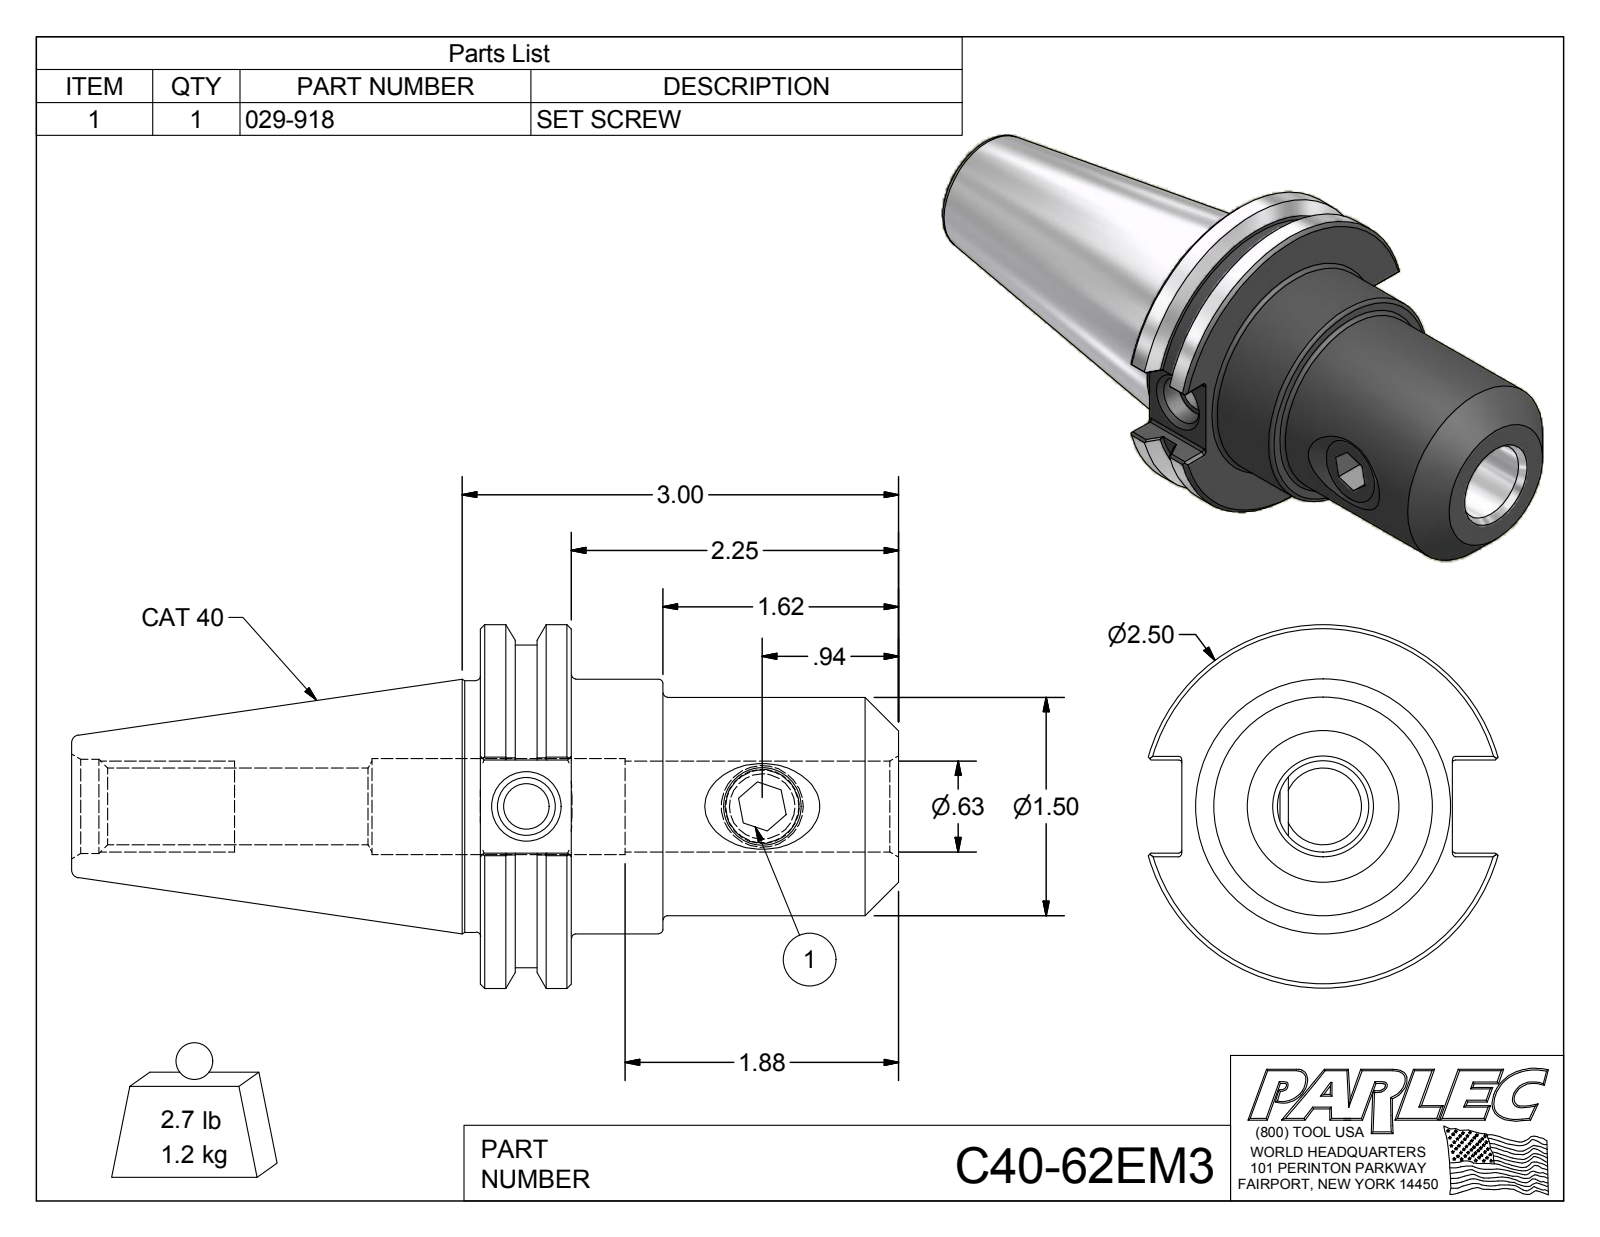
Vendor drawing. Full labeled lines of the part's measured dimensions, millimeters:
Part name (STEP PRODUCT): C40-62EM3; C40-62EM3-1; 029-918
STEP written by: Autodesk Inventor 2012 (AUTOMOTIVE_DESIGN)
Units: millimetres
Bodies: 2 solids, 105 faces (43 planar, 29 cylindrical, 33 other)
Overall size (bounding box): 144.4 × 63.5 × 61.1
Volume: 155 600 mm³ · Surface area: 31 180 mm²
Round holes (diameter × count): ⌀8 ×1, ⌀10.1 ×1, ⌀12.8 ×1, ⌀13.4 ×1, ⌀15.9 ×1, ⌀16.5 ×1, ⌀16.8 ×1
Round bosses / shafts (diameter × count): ⌀63.5 ×1, ⌀56.4 ×1, ⌀44.5 ×1, ⌀43.9 ×1, ⌀38.1 ×1, ⌀14.3 ×1
Partial cylindrical surfaces — rounded edges, fillets, slot ends (radius × count): R0.5 ×12
Main face-to-face distances: 15.9, 73, 57.2, 31.9, 16, 41.1, 16.3, 47.2, 71.4, 87.3
Hole centre spacings: 41.2
